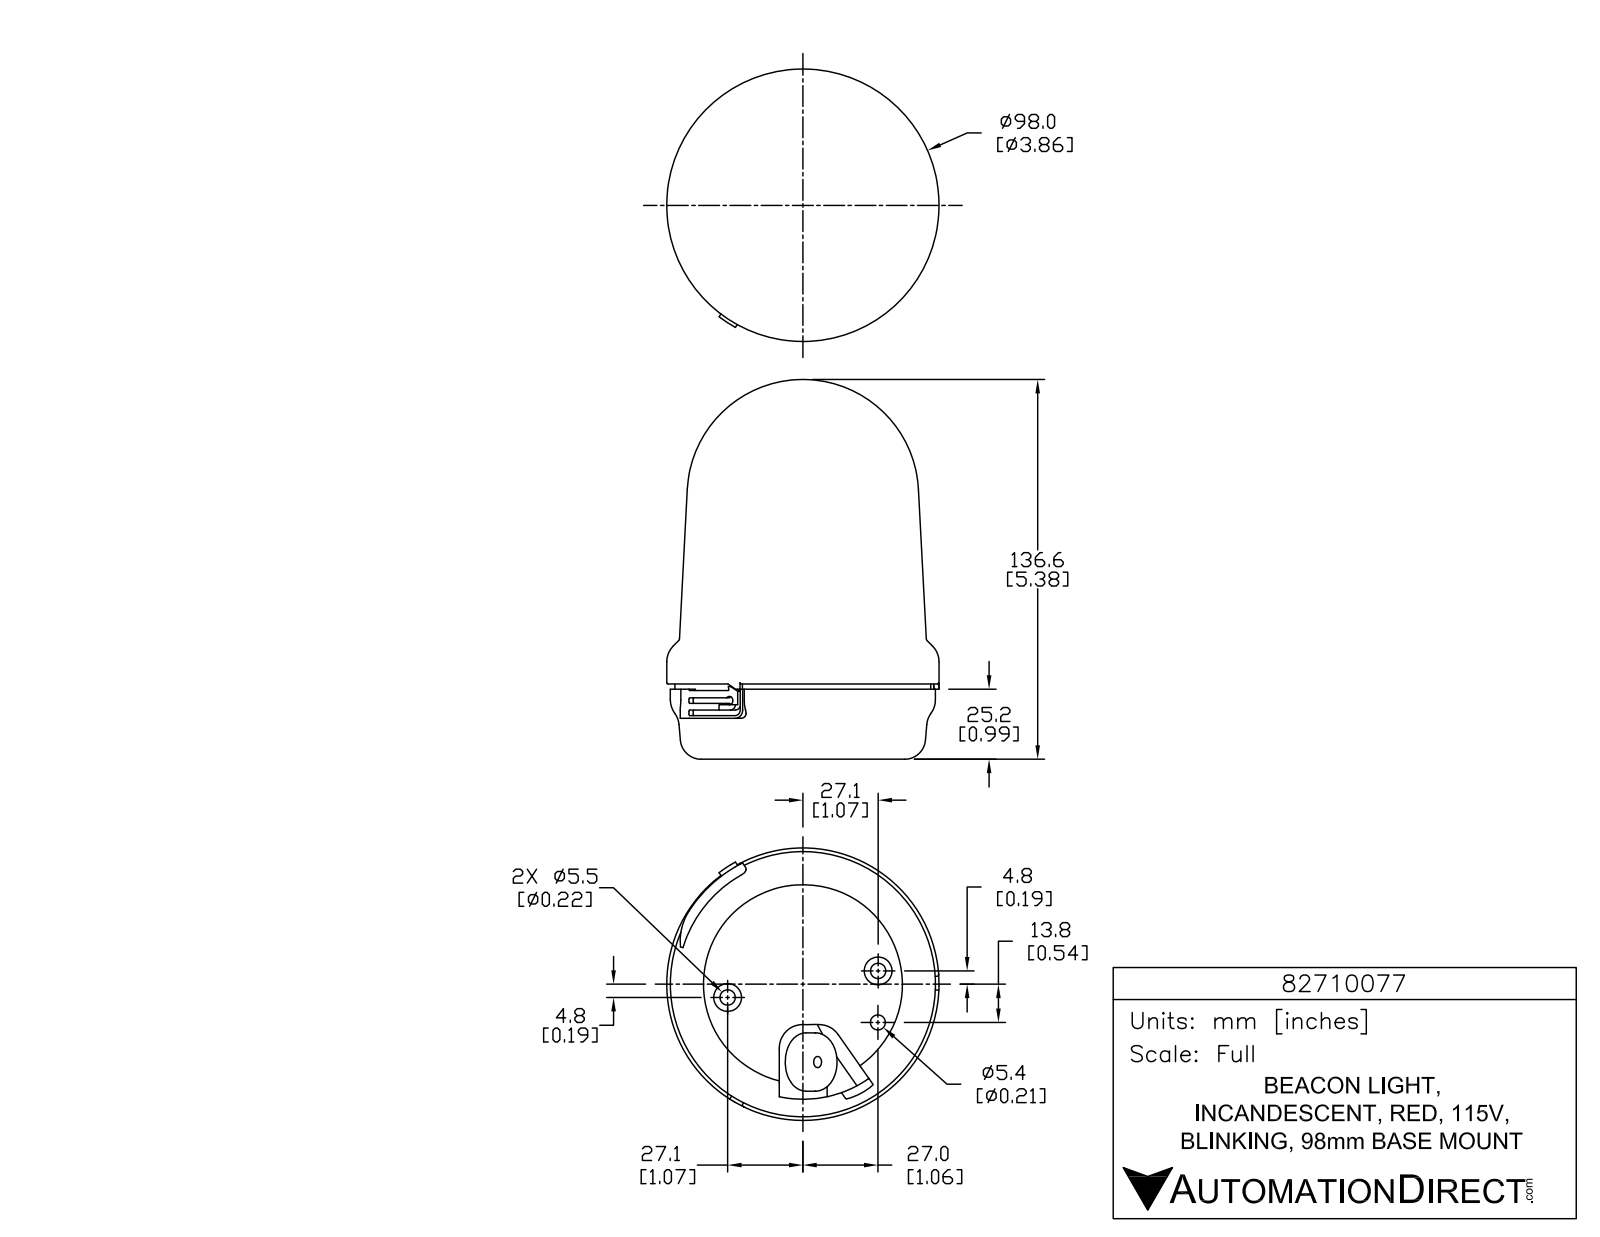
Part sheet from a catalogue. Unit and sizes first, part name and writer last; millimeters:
Units: millimetres
Overall size (bounding box): 136.6 × 98 × 98
Round holes (diameter × count): ⌀1.5 ×3, ⌀5.5 ×2, ⌀4 ×1, ⌀5.4 ×1, ⌀71.6 ×1
Round bosses / shafts (diameter × count): ⌀8.6 ×3, ⌀2.1 ×3, ⌀10 ×2, ⌀98 ×1, ⌀95.4 ×1, ⌀92.1 ×1, ⌀21 ×1
Partial cylindrical surfaces — rounded edges, fillets, slot ends (radius × count): R0.1 ×9, R0.1 ×6, R0.3 ×6, R0.3 ×6, R0.3 ×6, R5 ×6, R0.5 ×5, R1 ×4
Main face-to-face distances: 26.5, 24.7, 1.9, 0.5, 25.2, 27.1, 6, 14.7, 14.2, 10.5
Hole centre spacings: 27.5, 18.5, 30.3, 54.8, 55
Volume: 732 300 mm³ · Surface area: 47 520 mm²
Bodies: 1 solid, 872 faces (566 planar, 204 cylindrical, 102 other)
Part name (STEP PRODUCT): 82710077
STEP written by: SolidWorks 2015 (AUTOMOTIVE_DESIGN)
